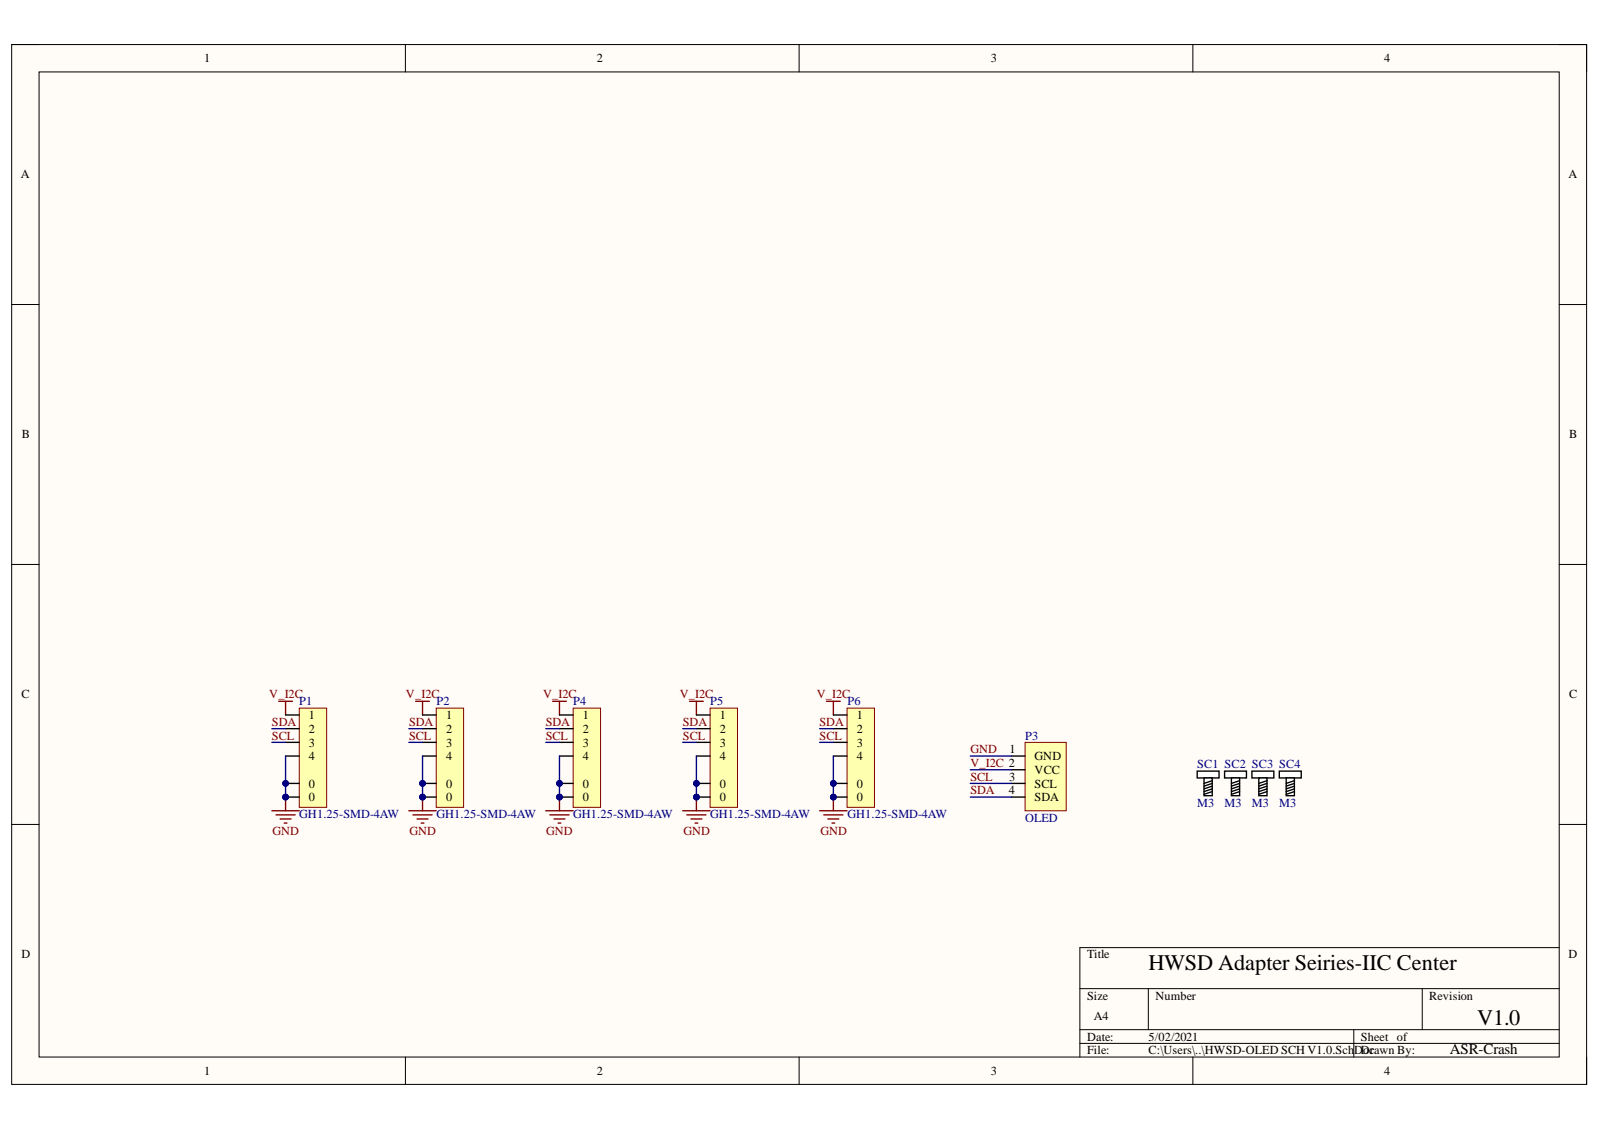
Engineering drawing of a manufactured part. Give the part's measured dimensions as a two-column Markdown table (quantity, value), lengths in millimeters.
| quantity | value |
| --- | --- |
| part name | PCB; Board; P6; JST_GH_SM04B-GHS-TB_1x04-1MP_P1.25mm_Horizontal (+7 more) |
| STEP written by | Open CASCADE 6.8 (AUTOMOTIVE_DESIGN) |
| units | millimeters |
| bodies | 15 solids, 1326 faces (1295 planar, 31 cylindrical, 0 other) |
| overall size | 40 × 20 × 11.54 |
| volume | 2 258 mm³ |
| surface area | 4 646 mm² |
| round holes (diameter × count) | 1 × 4, 3 × 4 |
| partial cylindrical surfaces (radius × count) | 0.2 × 9, 0.25 × 6, 2.54 × 4, 0.15 × 1, 0.35 × 1 |
| main face-to-face distances | 1.69, 6.77, 5.08, 8.03, 6.34, 1.26, 0.6, 6.35, 5.94, 4.25 |
| hole center spacings | 2.54, 5.08, 14.92, 34.92, 37.97, 3.6, 3.7, 6.14 |
